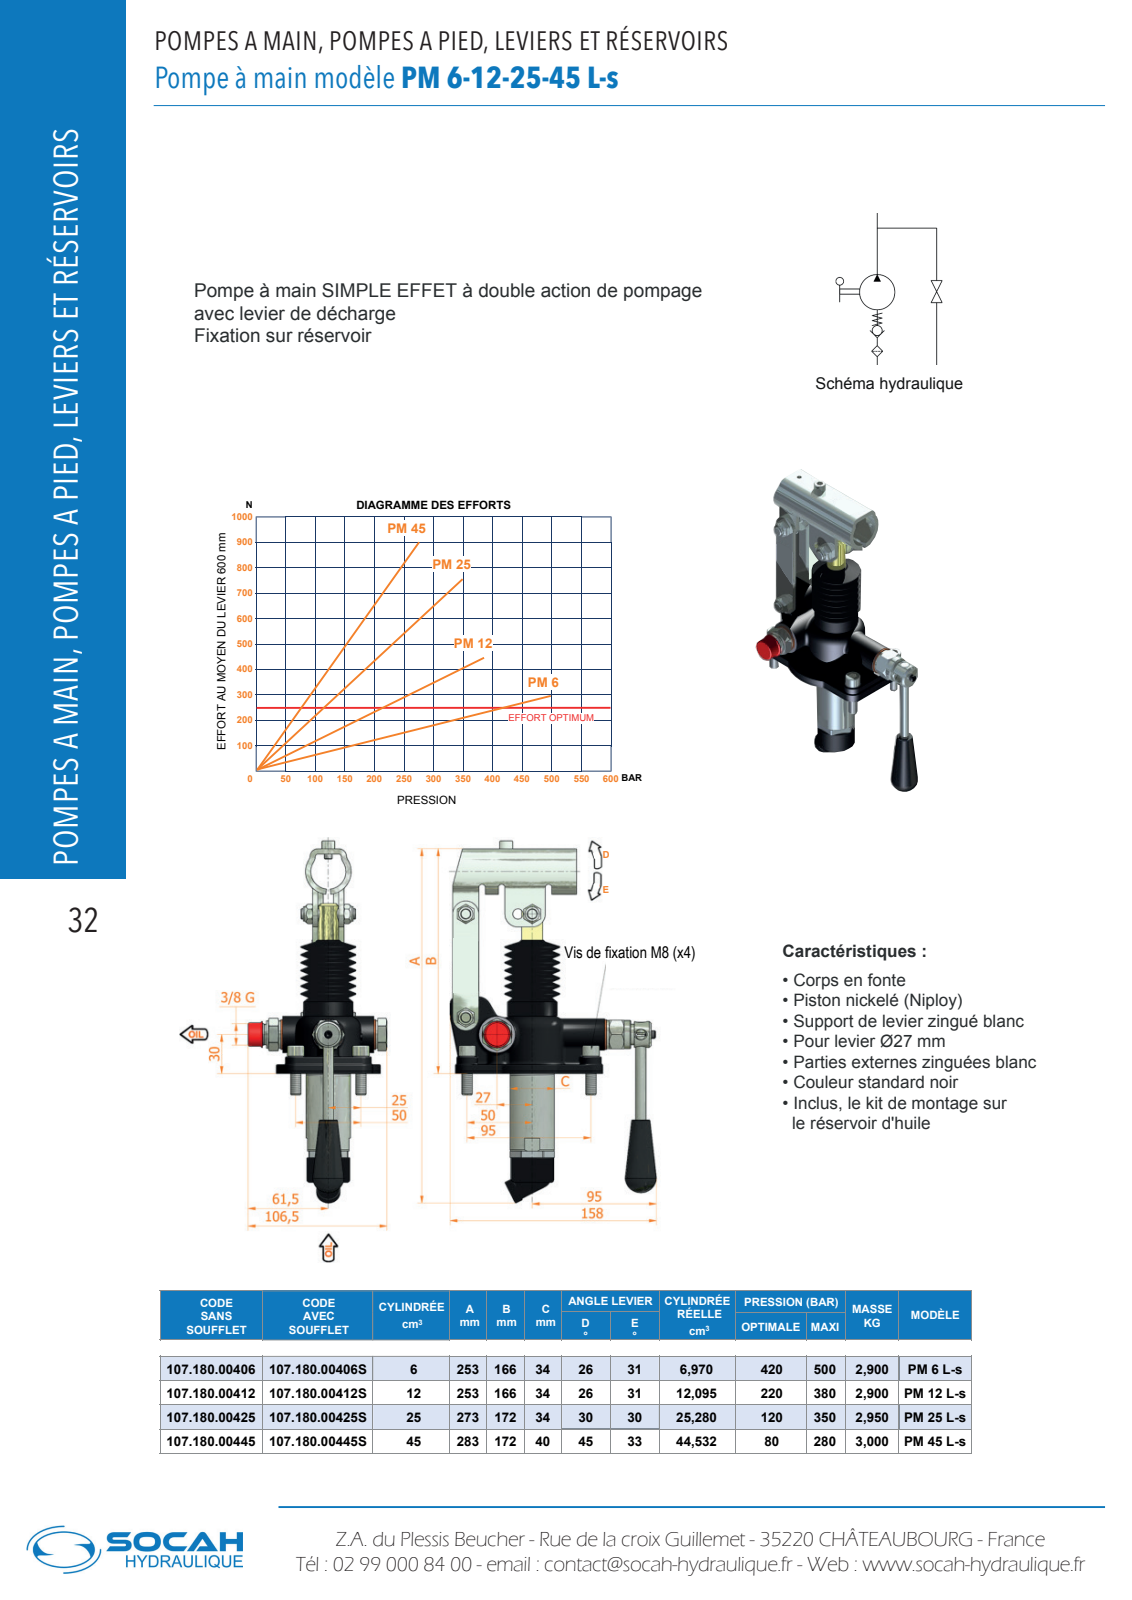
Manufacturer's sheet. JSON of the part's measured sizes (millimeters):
{"part_name": "6051.0122.00.50 Derivazione 2", "step_written_by": "Autodesk Inventor 2013 (AUTOMOTIVE_DESIGN)", "units": "millimeters", "bodies": {"solids": 12, "faces": 1468, "planar": 678, "cylindrical": 327, "other": 463}, "overall_size": [277.85, 158.22, 106.5], "round_holes": [[8, 7], [14, 4], [10, 2], [4, 1], [4.92, 1], [5, 1], [7.5, 1], [9, 1], [17, 1], [21, 1], [22, 1], [25, 1]], "round_bosses_or_shafts": [[13, 4], [12, 4], [8.5, 4], [8, 4], [20, 3], [18, 3], [16, 3], [11.05, 3]], "partial_cylinders_radius": [[1, 25], [0.2, 24], [3, 17], [0.1, 16], [2, 16], [8, 9], [0.36, 6], [0.53, 6]], "face_to_face_distances": [4, 20, 16, 2, 5, 7, 24, 13, 1, 95], "hole_center_spacings": [25.5, 26.1, 26.93, 45.67, 50, 51.48, 55.9, 88.6]}
